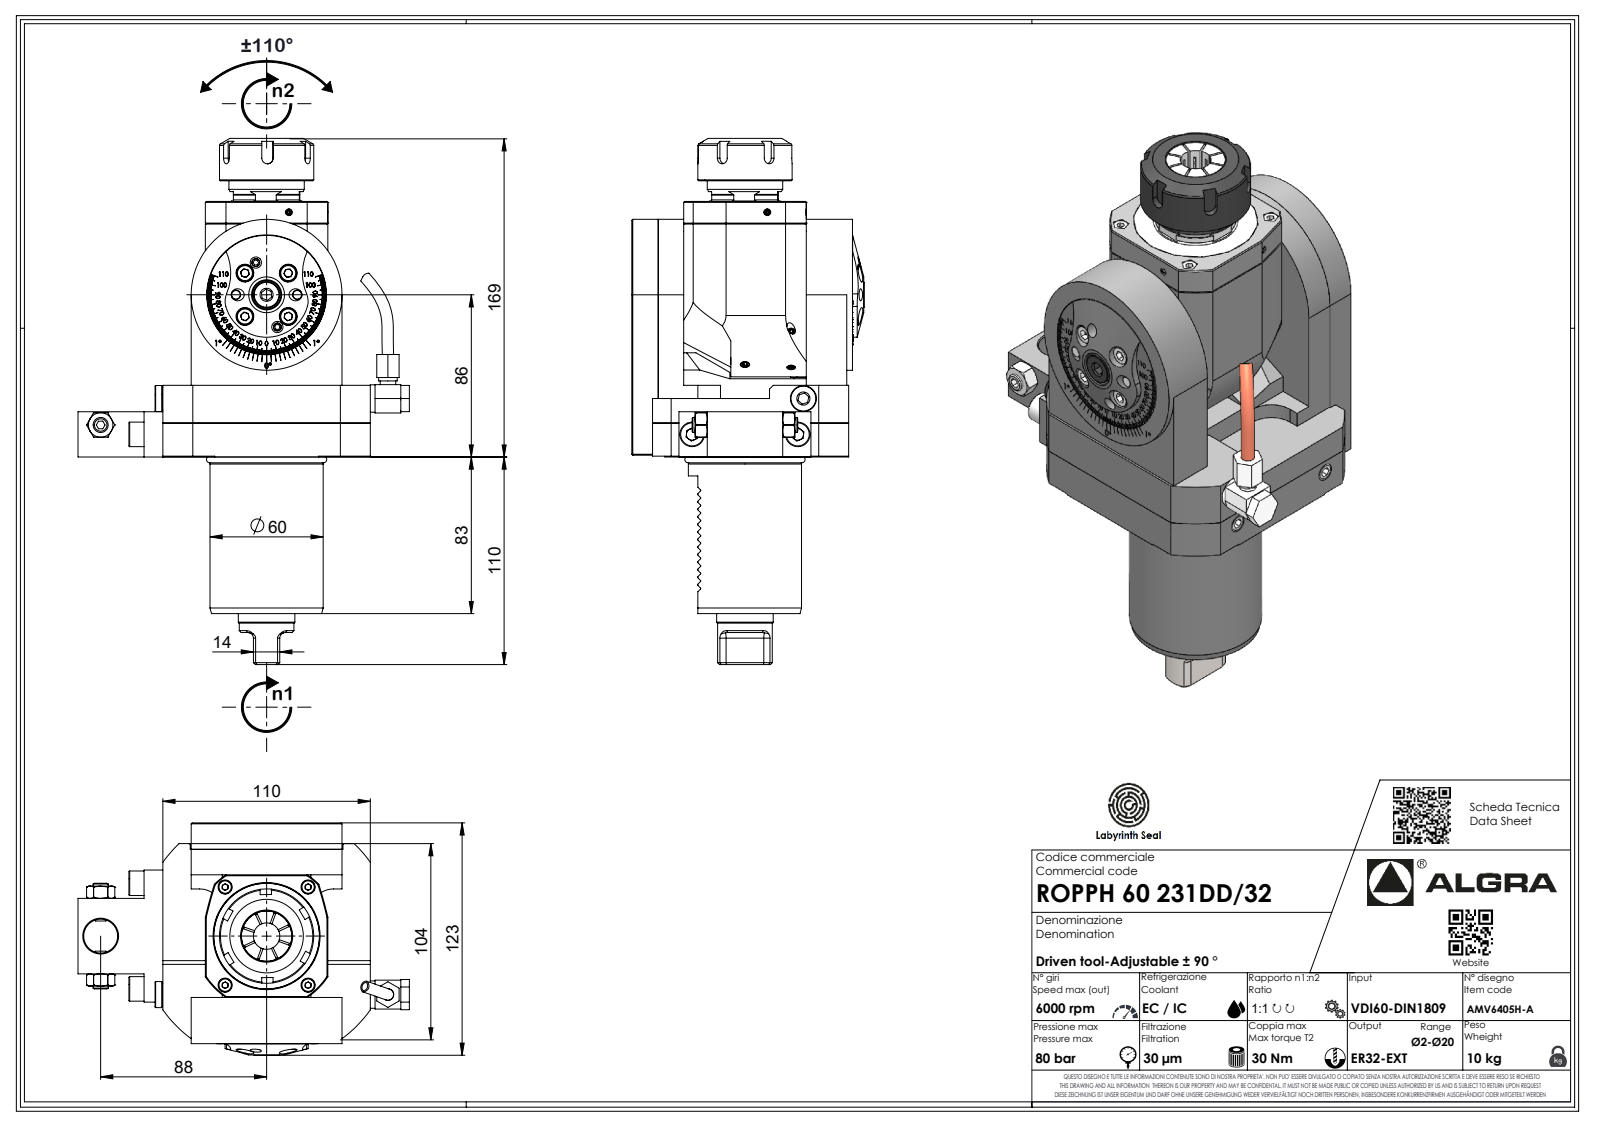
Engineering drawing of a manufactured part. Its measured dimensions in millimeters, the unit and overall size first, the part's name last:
Units: millimetres
Overall size (bounding box): 278.91 × 175.7 × 123
Round holes (diameter × count): ⌀2.1 ×1, ⌀5 ×1, ⌀44.2 ×1, ⌀48.2 ×1, ⌀52.2 ×1, ⌀56.2 ×1
Round bosses / shafts (diameter × count): ⌀80 ×1, ⌀60 ×1, ⌀58.7 ×1, ⌀56 ×1, ⌀52 ×1, ⌀50 ×1, ⌀48 ×1, ⌀44 ×1
Partial cylindrical surfaces — rounded edges, fillets, slot ends (radius × count): R0.3 ×14, R3 ×11, R0.33 ×7, R0.52 ×7, R3.7 ×7, R0.2 ×3, R10 ×2, R12 ×2
Main face-to-face distances: 22.5, 87.5, 65, 7, 80, 7.5, 27.5, 15, 72.5, 95
Volume: 1 461 000 mm³ · Surface area: 130 265 mm²
Bodies: 1 solid, 698 faces (434 planar, 115 cylindrical, 149 other)
Part name (STEP PRODUCT): ROPPH60231DD32
STEP written by: SolidWorks 2023 (AUTOMOTIVE_DESIGN)
